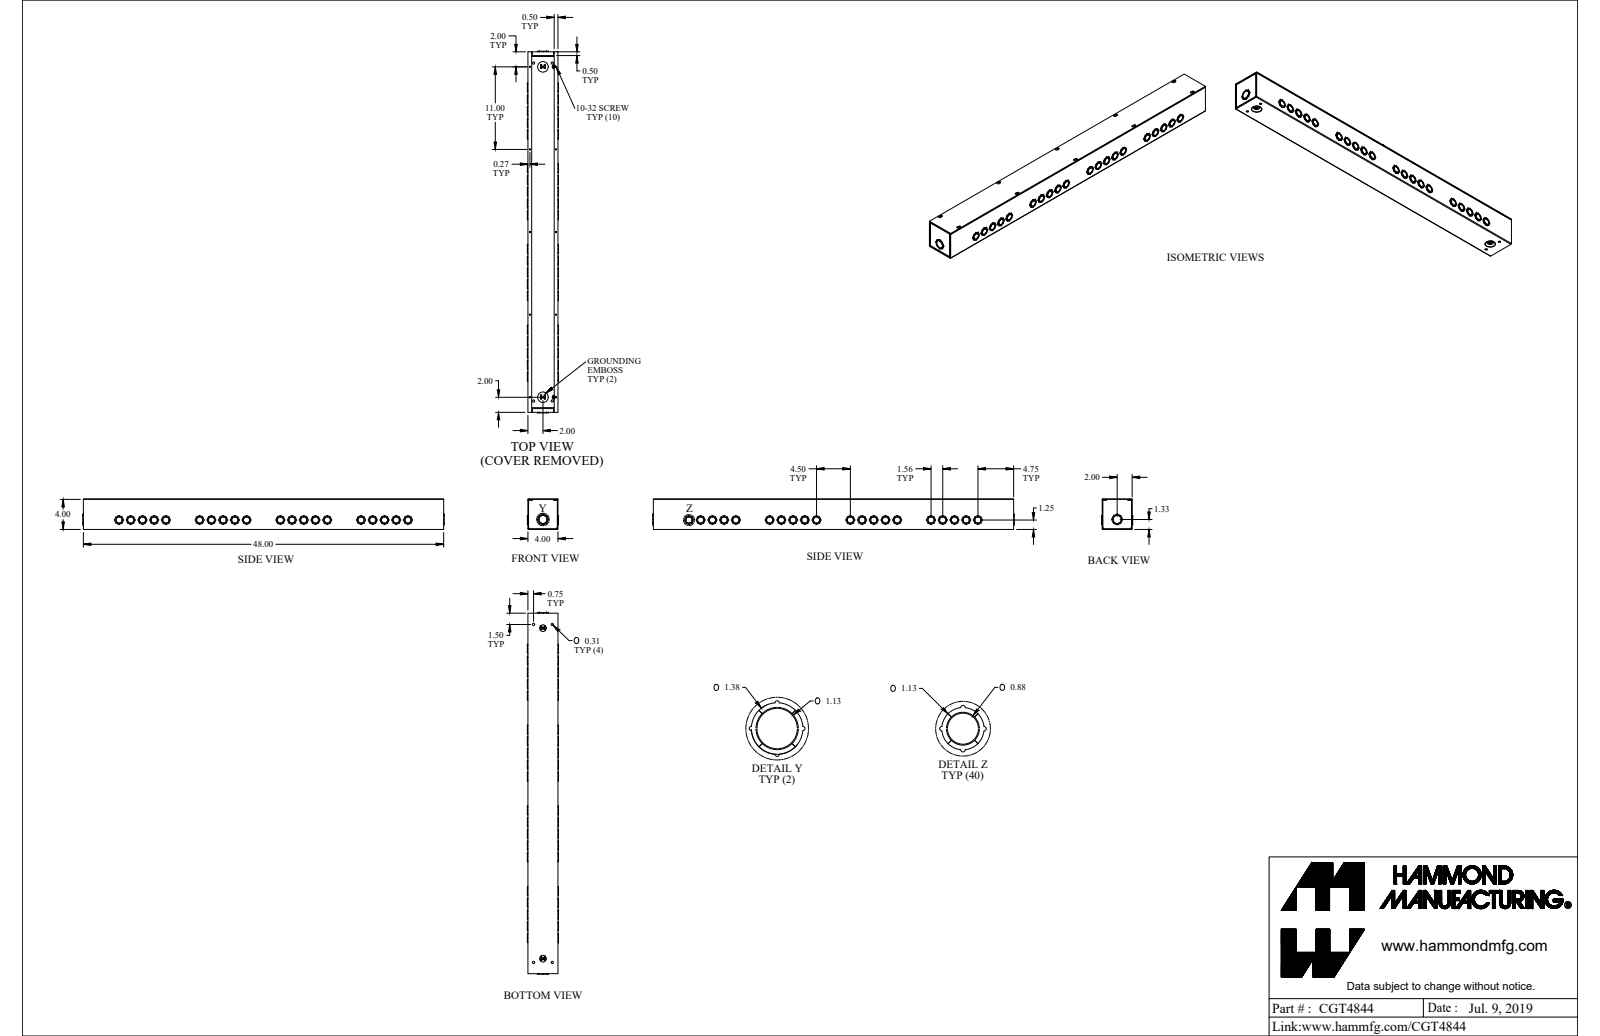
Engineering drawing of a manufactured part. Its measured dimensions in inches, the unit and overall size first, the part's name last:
Units: inches
Overall size (bounding box): 48.144 × 4.247 × 4.144
Round holes (diameter × count): ⌀0.875 ×20, ⌀0.17 ×12, ⌀0.312 ×4, ⌀0.5 ×2, ⌀1.125 ×1
Round bosses / shafts (diameter × count): ⌀1.125 ×20, ⌀0.825 ×20, ⌀0.492 ×2, ⌀0.375 ×2, ⌀0.284 ×2, ⌀0.19 ×2, ⌀1.375 ×1, ⌀1.075 ×1
Partial cylindrical surfaces — rounded edges, fillets, slot ends (radius × count): R0.062 ×80, R0.125 ×10, R0.203 ×10, R0.036 ×8, R0.057 ×8, R0.108 ×8, R0.029 ×4, R0.057 ×4
Main face-to-face distances: 0.057, 3.943, 4, 0.072, 3.886, 4.072, 4.015, 0.129, 47.928, 4.144
Hole centre spacings: 10.748, 3.124, 1.562, 1.562, 7.624, 9.186, 11, 11.531
Volume: 54.53 in³ · Surface area: 1 736 in²
Bodies: 6 solids, 2038 faces (930 planar, 1094 cylindrical, 14 other)
Part name (STEP PRODUCT): CGT4844
STEP written by: SolidWorks 2021 (AUTOMOTIVE_DESIGN)
